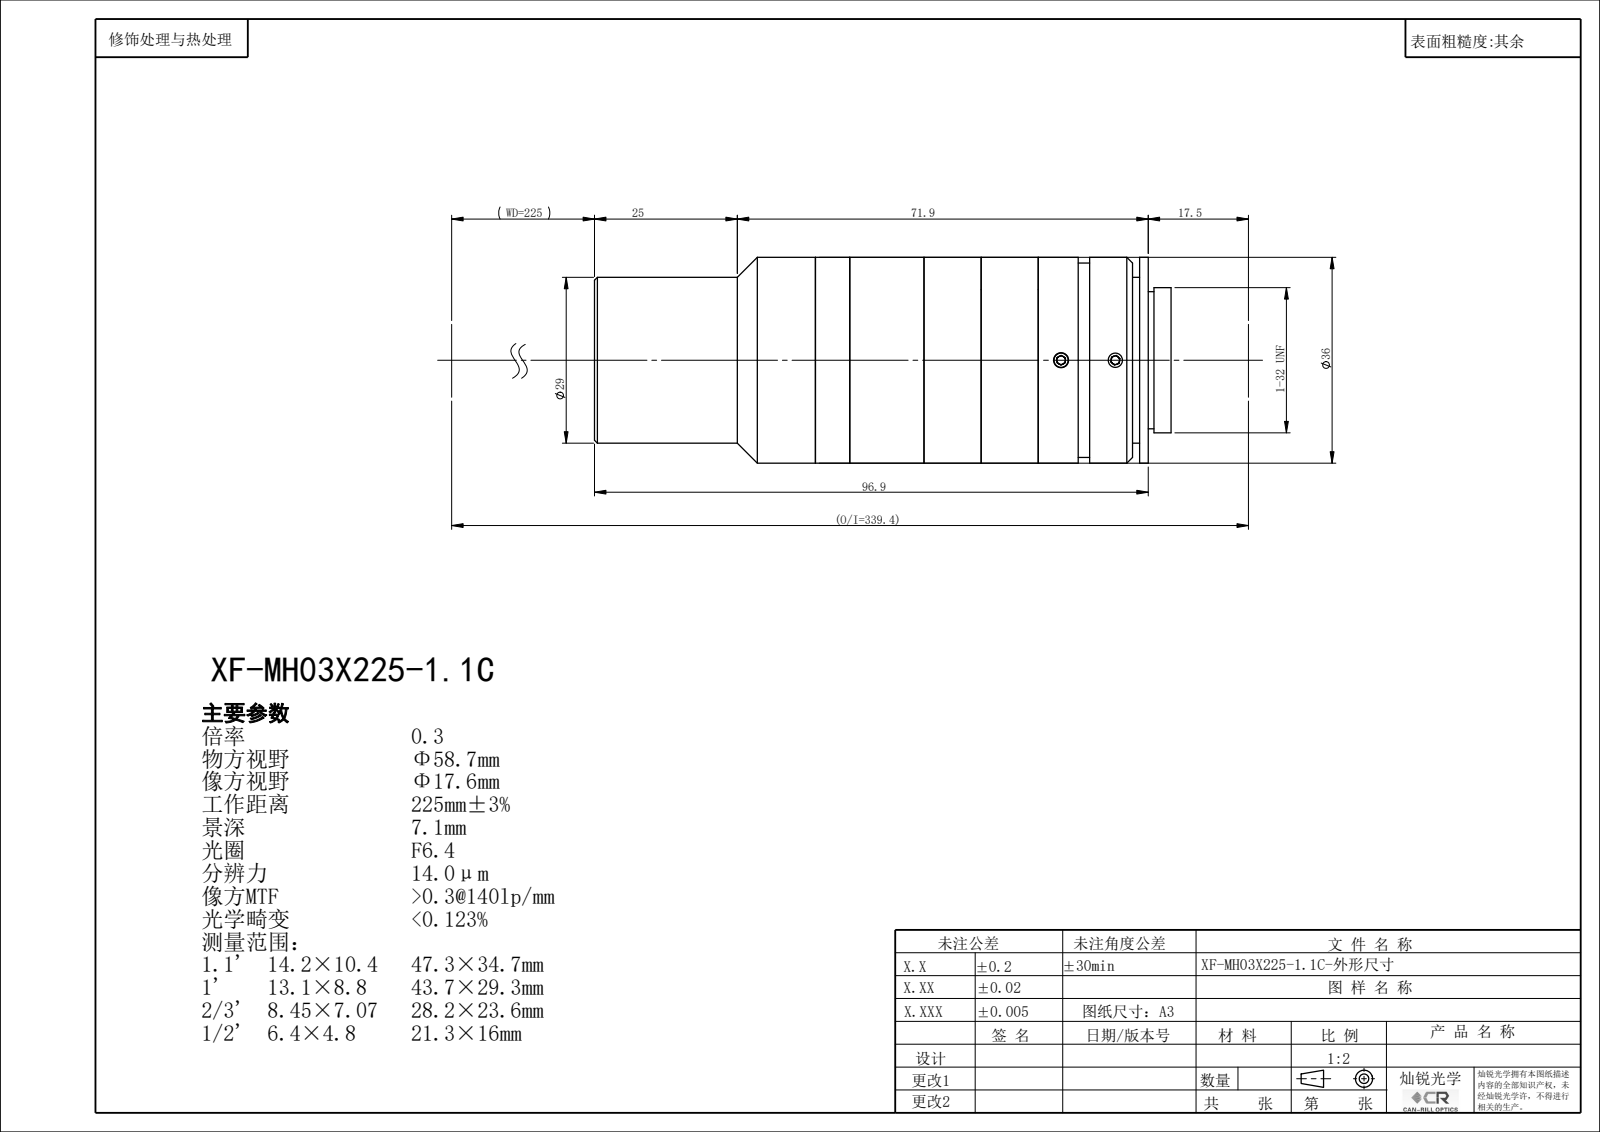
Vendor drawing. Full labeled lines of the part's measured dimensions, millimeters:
Part name (STEP PRODUCT): XF-MH03X225-1.1C
STEP written by: SolidWorks 2022 (CONFIG_CONTROL_DESIGN)
Units: millimetres
Bodies: 0 solids, 142 faces (70 planar, 44 cylindrical, 28 other)
Overall size (bounding box): 100.94 × 36 × 36
Round holes (diameter × count): ⌀2.5 ×3, ⌀20 ×1, ⌀22.4 ×1, ⌀24 ×1, ⌀24.9 ×1, ⌀26 ×1, ⌀26.4 ×1
Round bosses / shafts (diameter × count): ⌀36 ×1, ⌀34 ×1, ⌀29 ×1, ⌀25.4 ×1
Main face-to-face distances: 10, 19.25, 1.5, 17.75, 27.75, 29.25, 20, 37.75, 39.25, 36.5
